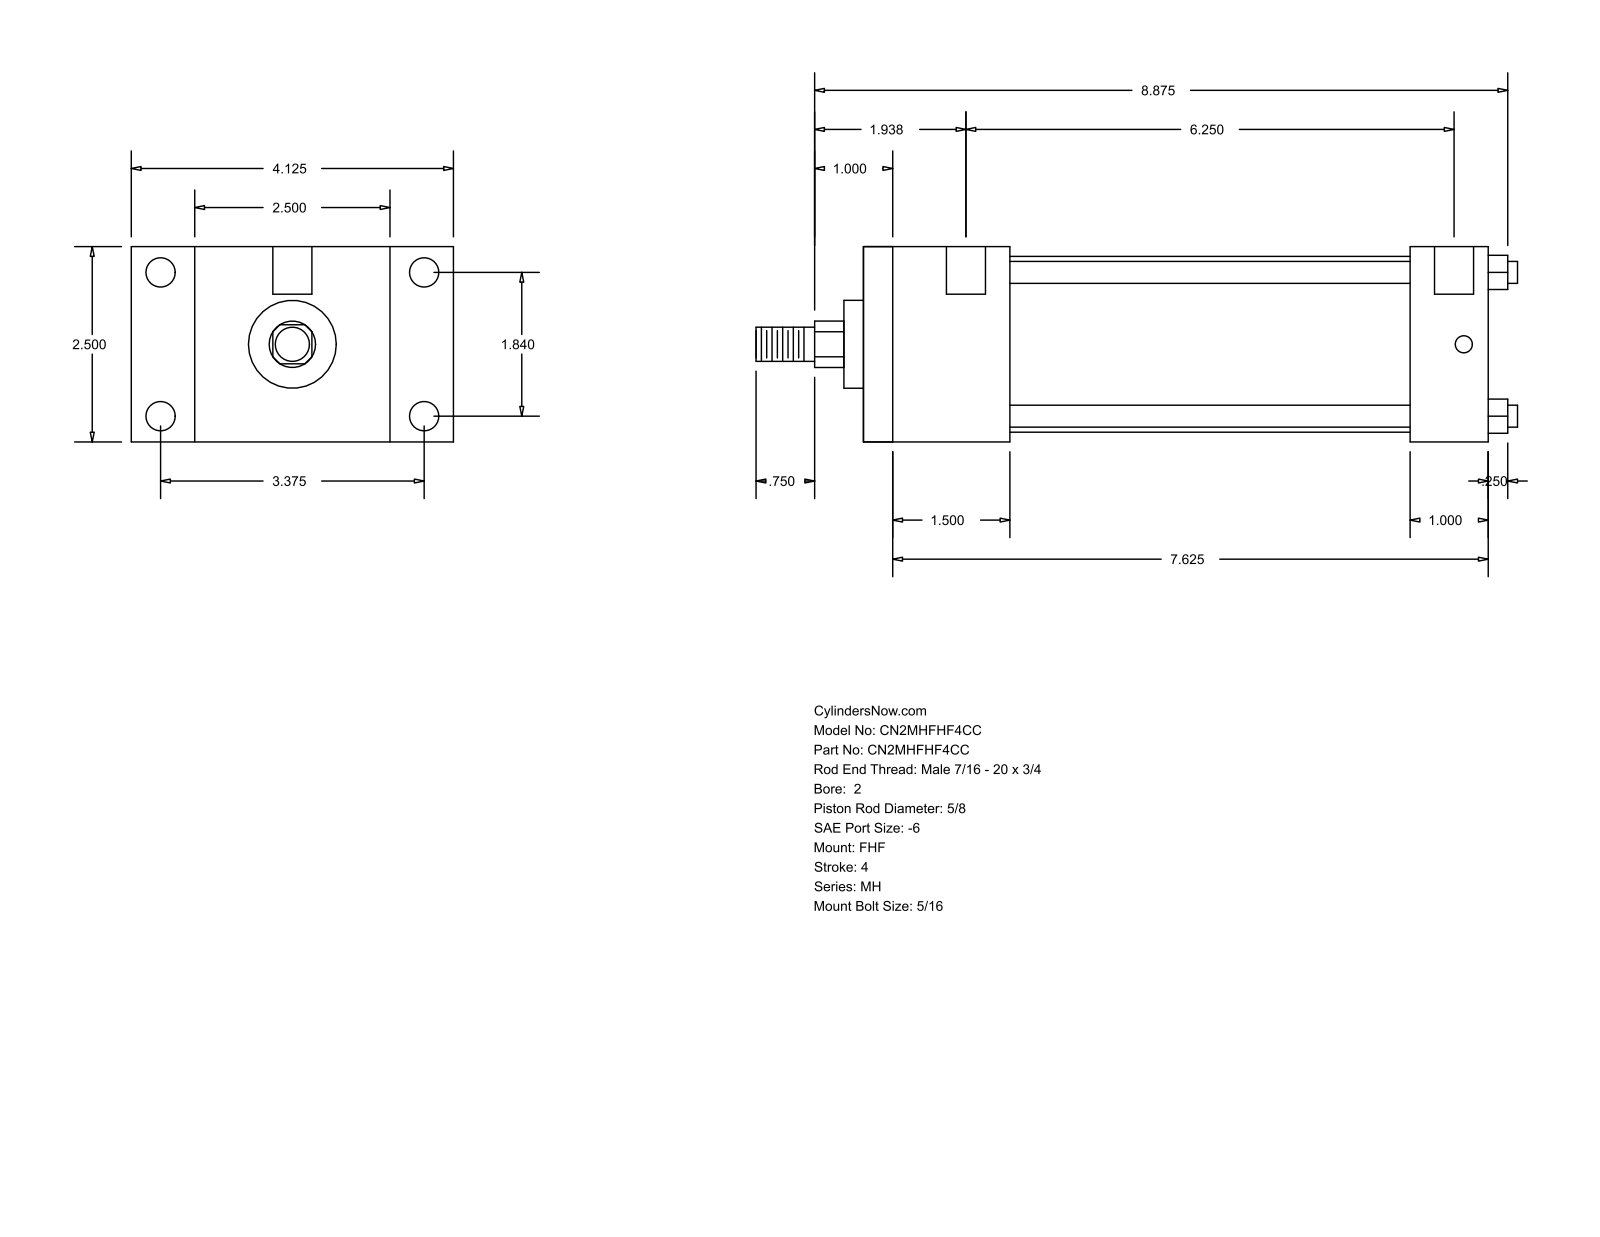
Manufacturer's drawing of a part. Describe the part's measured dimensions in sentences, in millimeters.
The part is named "MH_FHF__0200_0.625". Its 3-D file was written by "GSSL Pune (CONFIG_CONTROL_DESIGN)". It is 0 solids with 88 faces: 60 planar, 28 cylindrical and 0 other. Overall it measures 247.65 by 104.78 by 63.5 millimeters. Round holes: 4 of diameter 5.56, 4 of diameter 9.53, 2 of diameter 12.7. Round bosses or shafts: 4 of diameter 7.14, 1 of diameter 57.15, 1 of diameter 28.57, 1 of diameter 15.88, 1 of diameter 11.11. Partial cylindrical surfaces (rounded edges, fillets, slot ends): 1 of radius 7.54. The main face-to-face distances are 63.5, 47.62, 203.19, 155.57, 20.64, 84.14, 104.78, 177.8, 130.18, 25.39. The hole center spacings are 46.74, 85.72, 97.63, 166.69, 3.18, 4.76, 158.75, 161.93.
